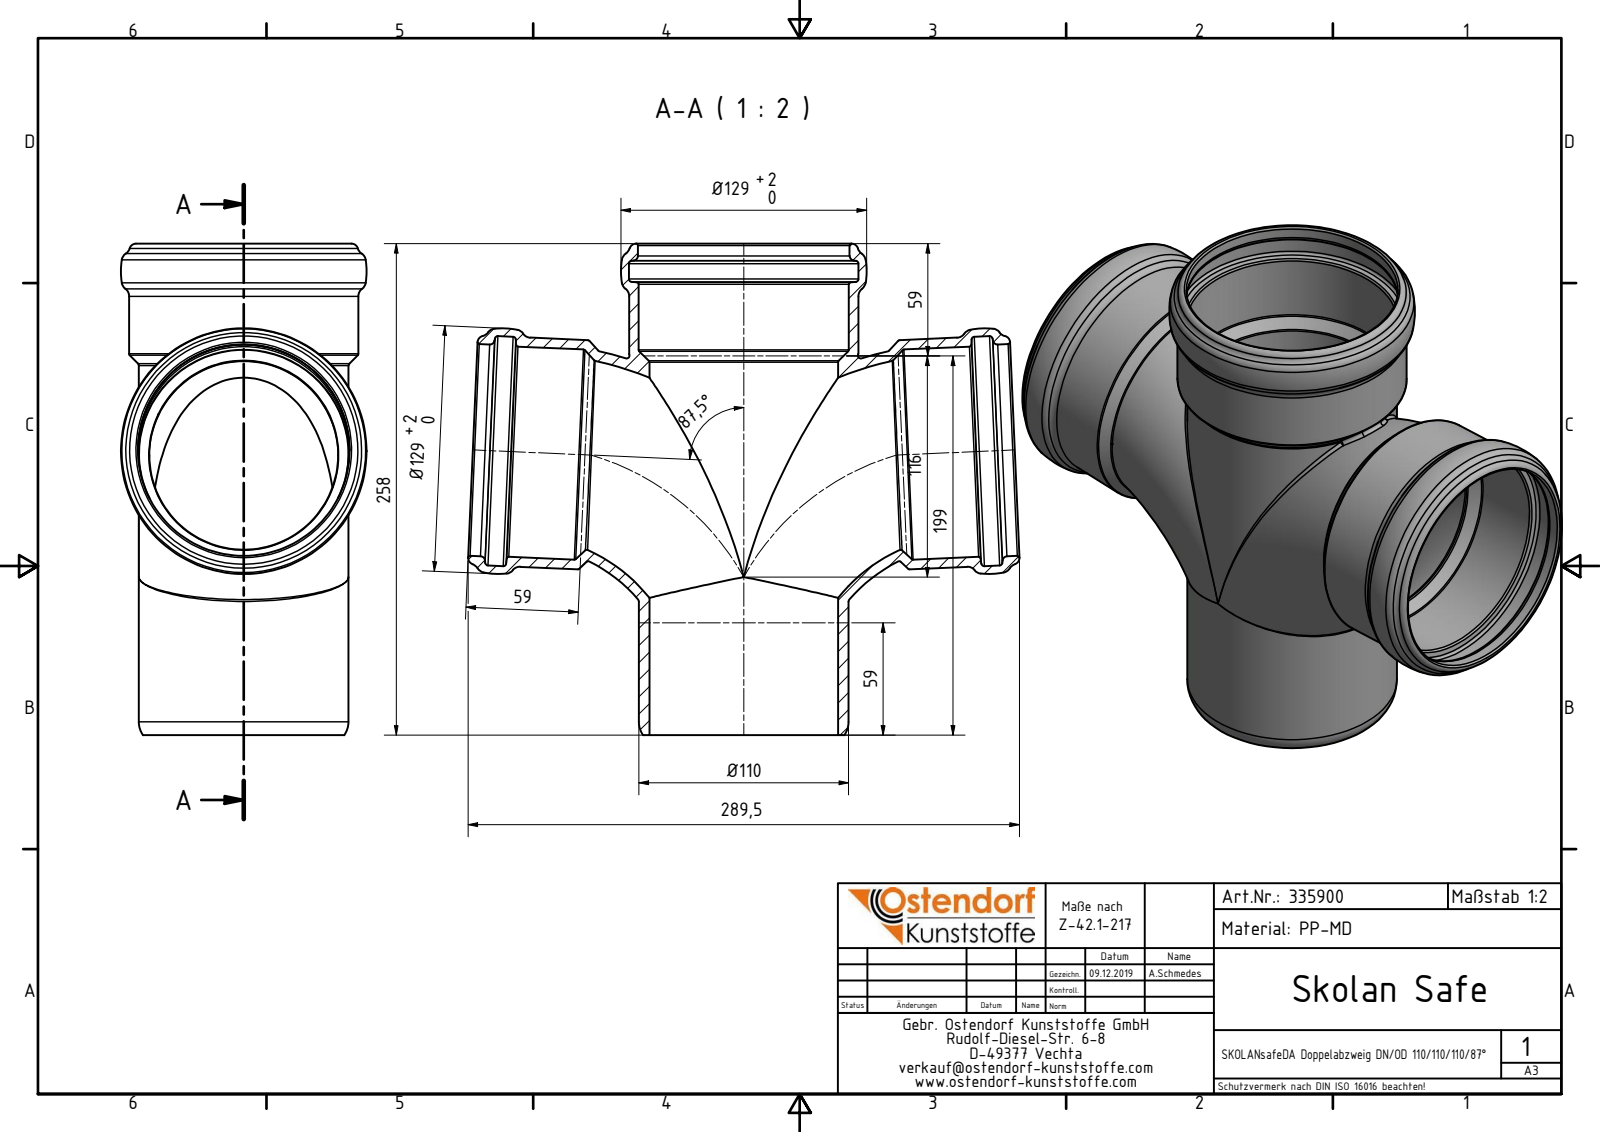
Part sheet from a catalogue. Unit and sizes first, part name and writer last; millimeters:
Units: millimetres
Overall size (bounding box): 289.53 × 258 × 129
Round holes (diameter × count): ⌀110.4 ×3, ⌀111.2 ×3, ⌀120.6 ×3, ⌀99.1 ×1
Round bosses / shafts (diameter × count): ⌀120.4 ×3, ⌀110.1 ×1
Volume: 765 197 mm³ · Surface area: 302 841 mm²
Bodies: 1 solid, 102 faces (1 planar, 17 cylindrical, 84 other)
Part name (STEP PRODUCT): 335900 SKOLANsafeDA Doppelabzweiger DN_OD 110_110_110_87°
STEP written by: Autodesk Inventor 2020 (AUTOMOTIVE_DESIGN)
